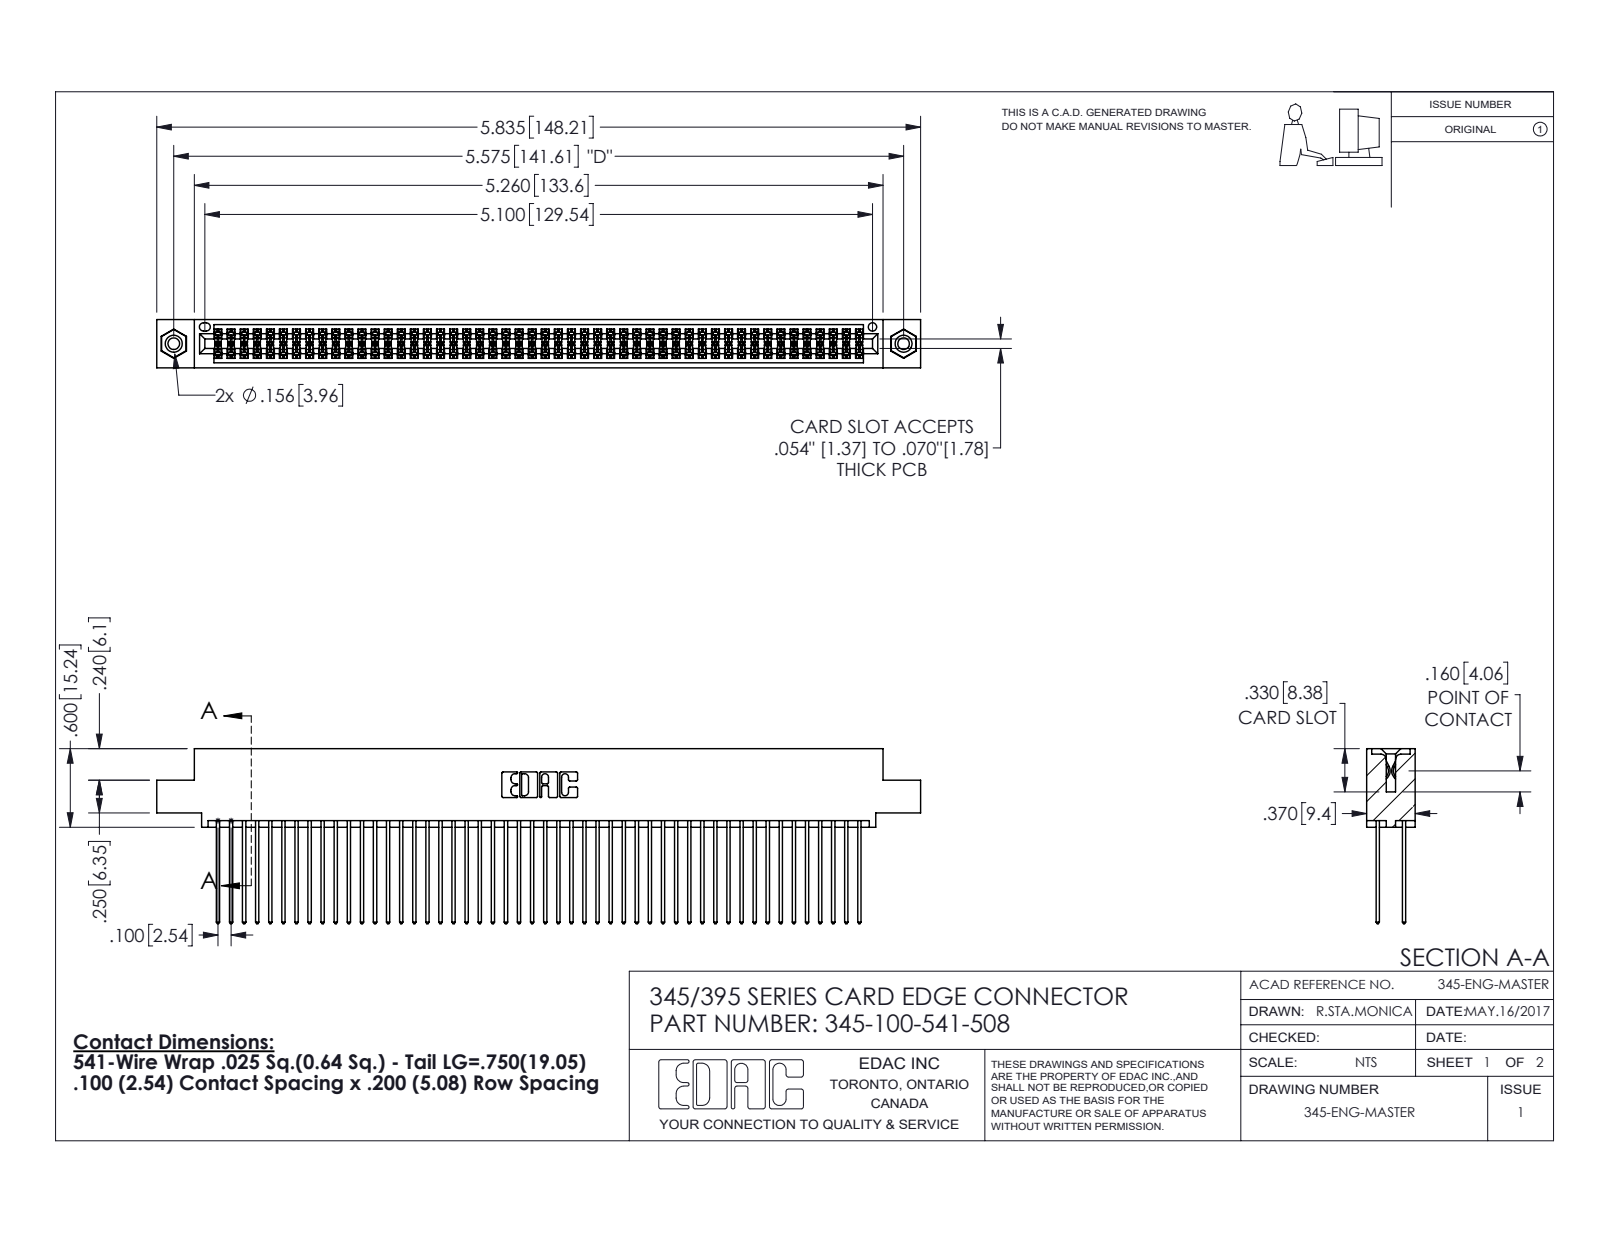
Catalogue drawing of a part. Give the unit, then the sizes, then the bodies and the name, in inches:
Units: inches
Overall size (bounding box): 5.835 × 1.337 × 0.37
Round holes (diameter × count): ⌀0.089 ×2, ⌀0.125 ×2, ⌀0.156 ×2, ⌀0.064 ×1
Round bosses / shafts (diameter × count): ⌀0.155 ×2
Partial cylindrical surfaces — rounded edges, fillets, slot ends (radius × count): R0.006 ×150, R0.01 ×100, R0.01 ×22, R0.007 ×6, R0.031 ×6, R0.026 ×3, R0.014 ×2, R0.019 ×2
Main face-to-face distances: 0.072, 0.298, 0.2, 0.098, 0.272, 0.025, 0.225, 0.37, 0.175, 0.149
Hole centre spacings: 0.27, 5.339, 5.575
Volume: 0.913 in³ · Surface area: 38.87 in²
Bodies: 103 solids, 5190 faces (3416 planar, 1758 cylindrical, 16 other)
Part name (STEP PRODUCT): 345-100-541-508; 345-250-001_345-250-003-102; 345-292-001_345-293-141; 345 Part_0.110 Offset - 0.156 Dia-TI
STEP written by: SolidWorks 2016 (CONFIG_CONTROL_DESIGN)
